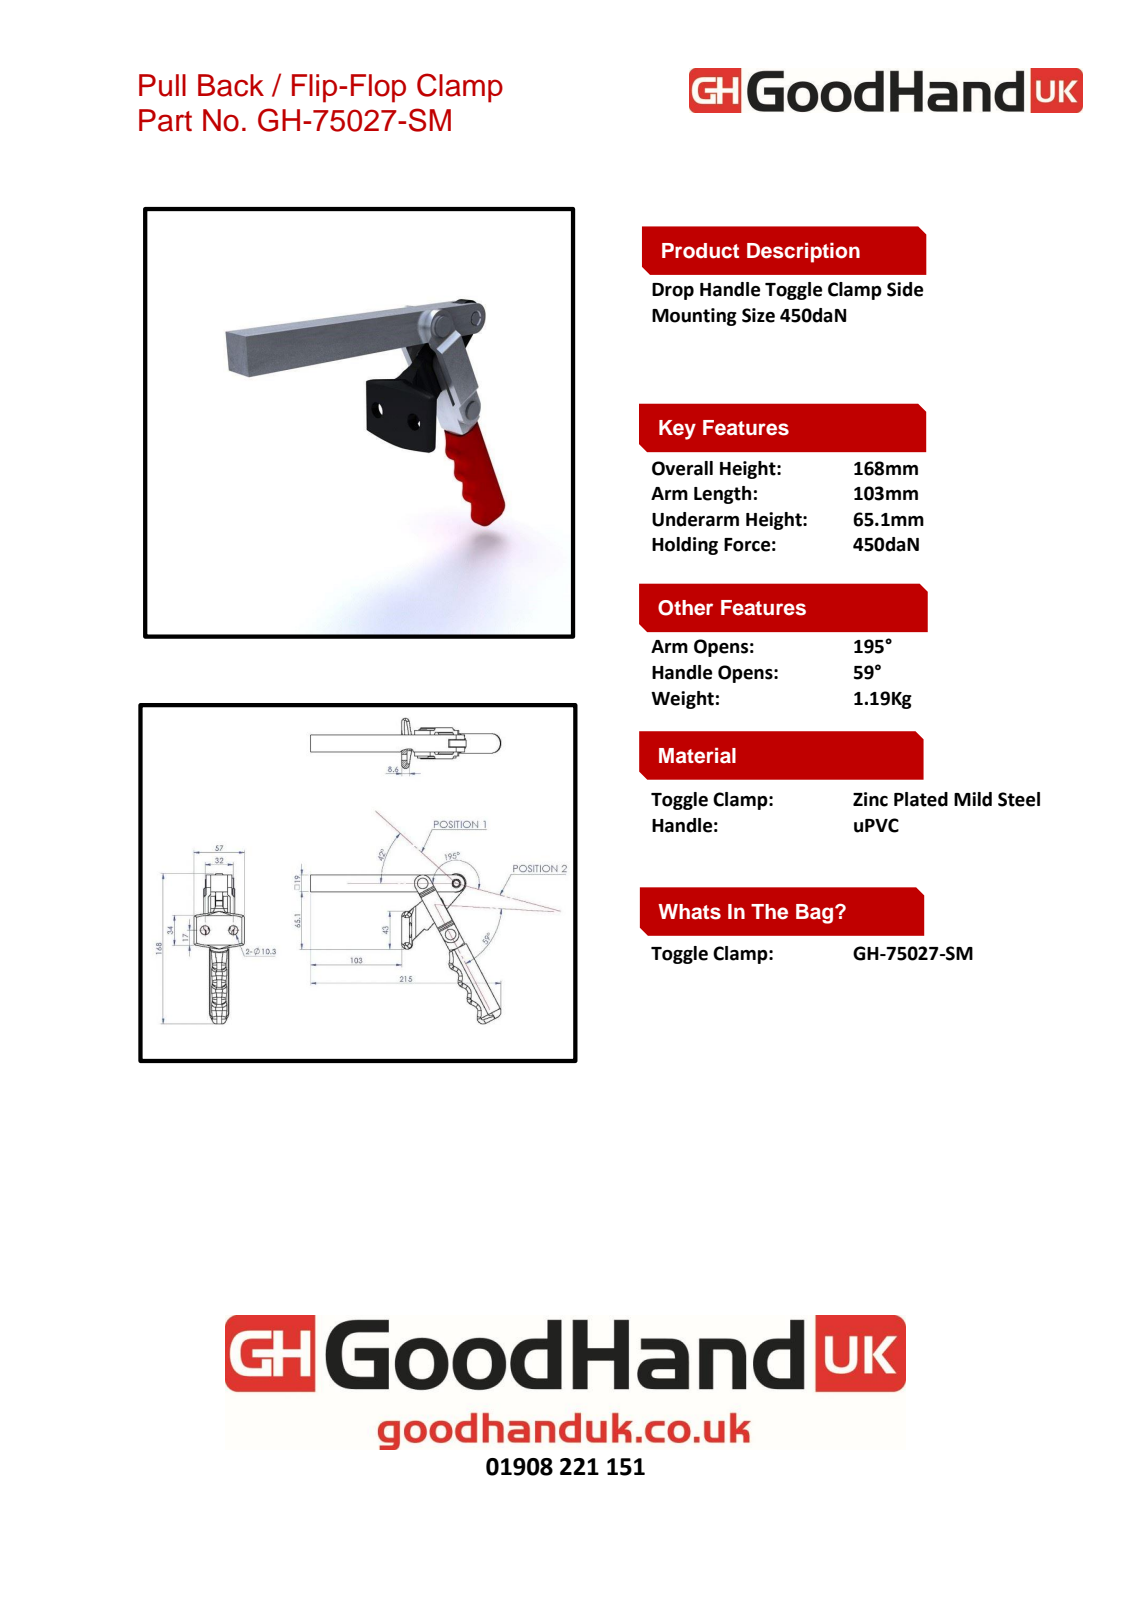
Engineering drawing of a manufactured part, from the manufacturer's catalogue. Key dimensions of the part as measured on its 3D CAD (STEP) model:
Part name (STEP PRODUCT): Group1^GH-75027-SM(簡化)-1; Group2^GH-75027-SM(簡化)-1; Group3^GH-75027-SM(簡化)-1; GH-75027-SM(簡化)-1 (+1 more)
STEP written by: SolidWorks 2016 (AUTOMOTIVE_DESIGN)
Units: millimetres
Bodies: 4 solids, 265 faces (72 planar, 116 cylindrical, 77 other)
Overall size (bounding box): 214.63 × 170.5 × 57
Volume: 166 800 mm³ · Surface area: 48 815 mm²
Round holes (diameter × count): ⌀6 ×4, ⌀10.3 ×2, ⌀17.1 ×2
Round bosses / shafts (diameter × count): ⌀20 ×2, ⌀10 ×2, ⌀7 ×2
Partial cylindrical surfaces — rounded edges, fillets, slot ends (radius × count): R2 ×16, R3 ×12, R20 ×7, R5 ×6, R7 ×4, R9.5 ×4, R0.5 ×3, R4.31 ×2
Main face-to-face distances: 19, 5, 4.9, 14.1, 3, 27, 22, 8, 0.65, 8.45
Hole centre spacings: 32, 27.87, 34.16, 38, 38.14, 58.35, 65.99
